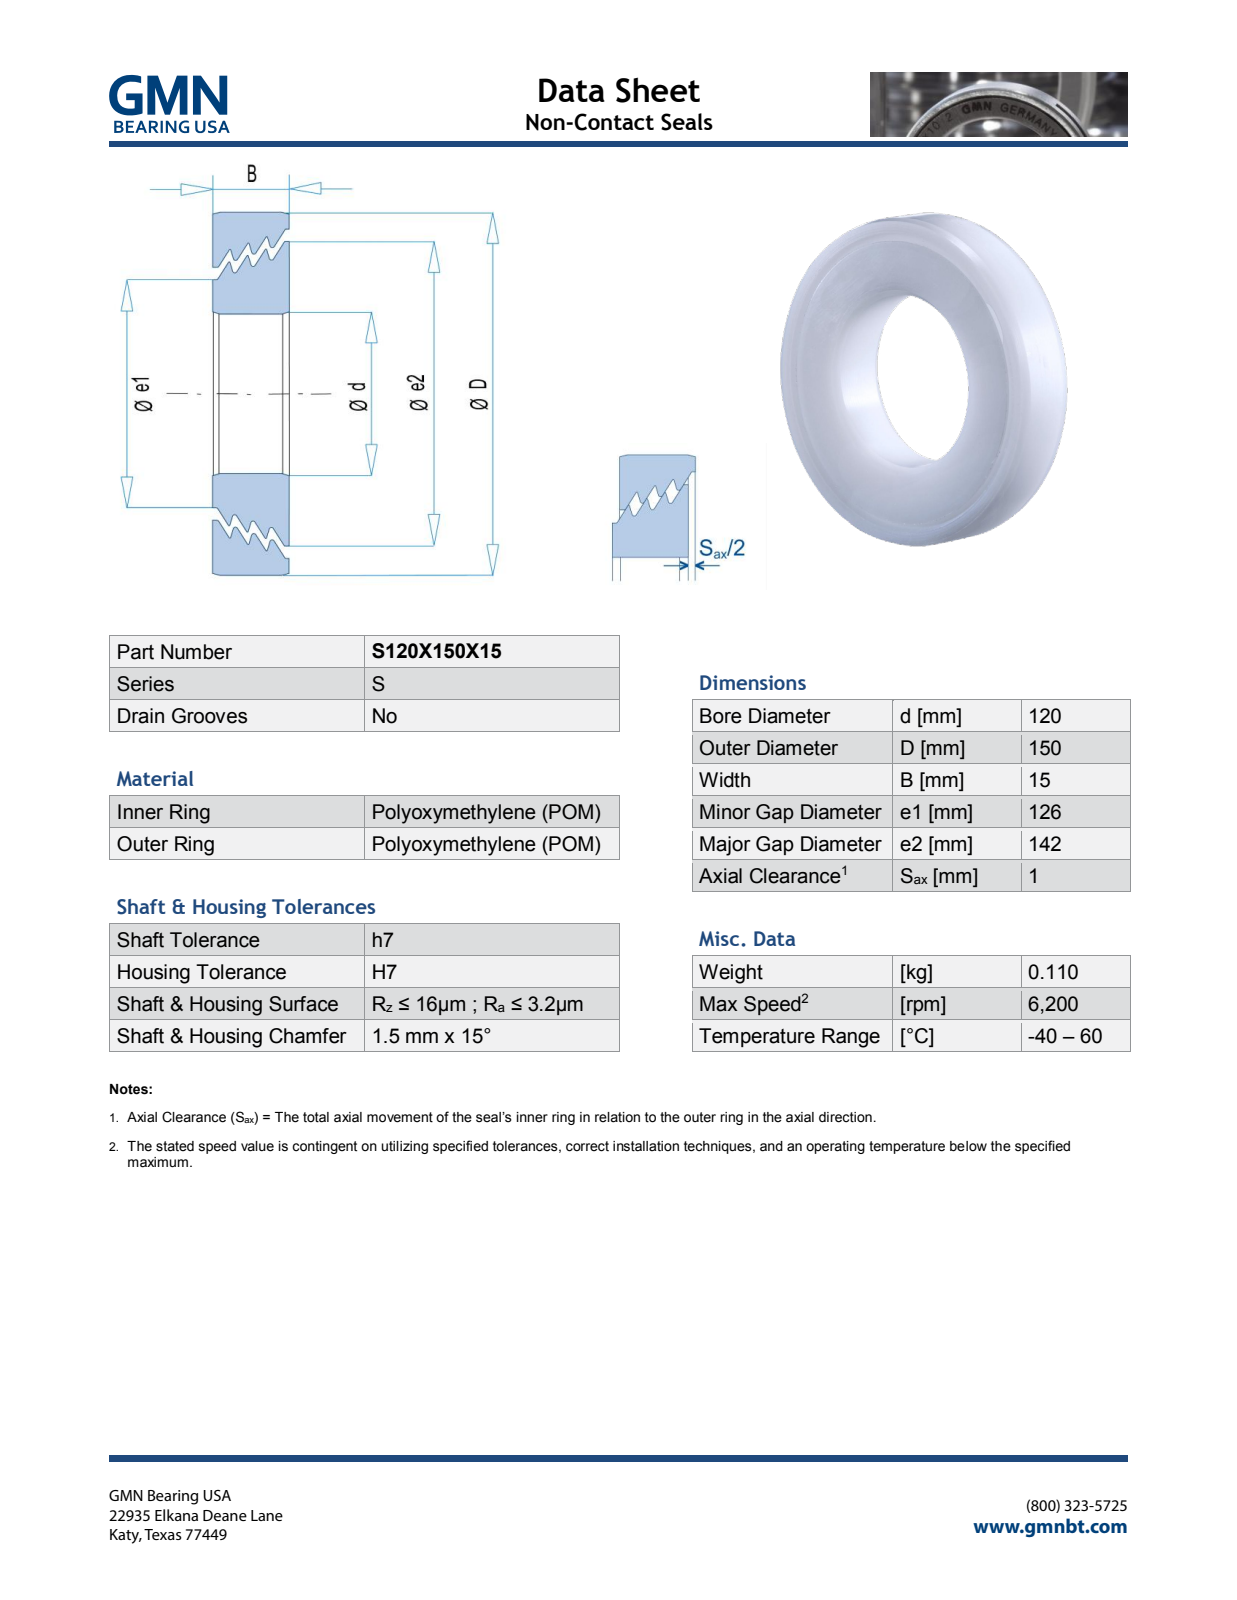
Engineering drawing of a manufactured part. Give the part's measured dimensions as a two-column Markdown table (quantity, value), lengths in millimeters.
| quantity | value |
| --- | --- |
| part name | S120X150X15_PRT |
| STEP written by | PRO/ENGINEER BY PARAMETRIC TECHNOLOGY CORPORATION, 2013150 (AUTOMOTIVE_DESIGN) |
| units | millimeters |
| bodies | 2 solids, 682 faces (586 planar, 12 cylindrical, 84 other) |
| overall size | 150 × 150 × 15.07 |
| volume | 88 286 mm³ |
| surface area | 47 151 mm² |
| round holes (diameter × count) | 120 × 1, 127.63 × 1, 143.63 × 1 |
| round bosses / shafts (diameter × count) | 150 × 1, 142 × 1, 126 × 1 |
| main face-to-face distances | 15, 15.07, 2.15, 1.88, 2.14, 1.52, 1.61, 1.87, 0.96, 1.79 |
